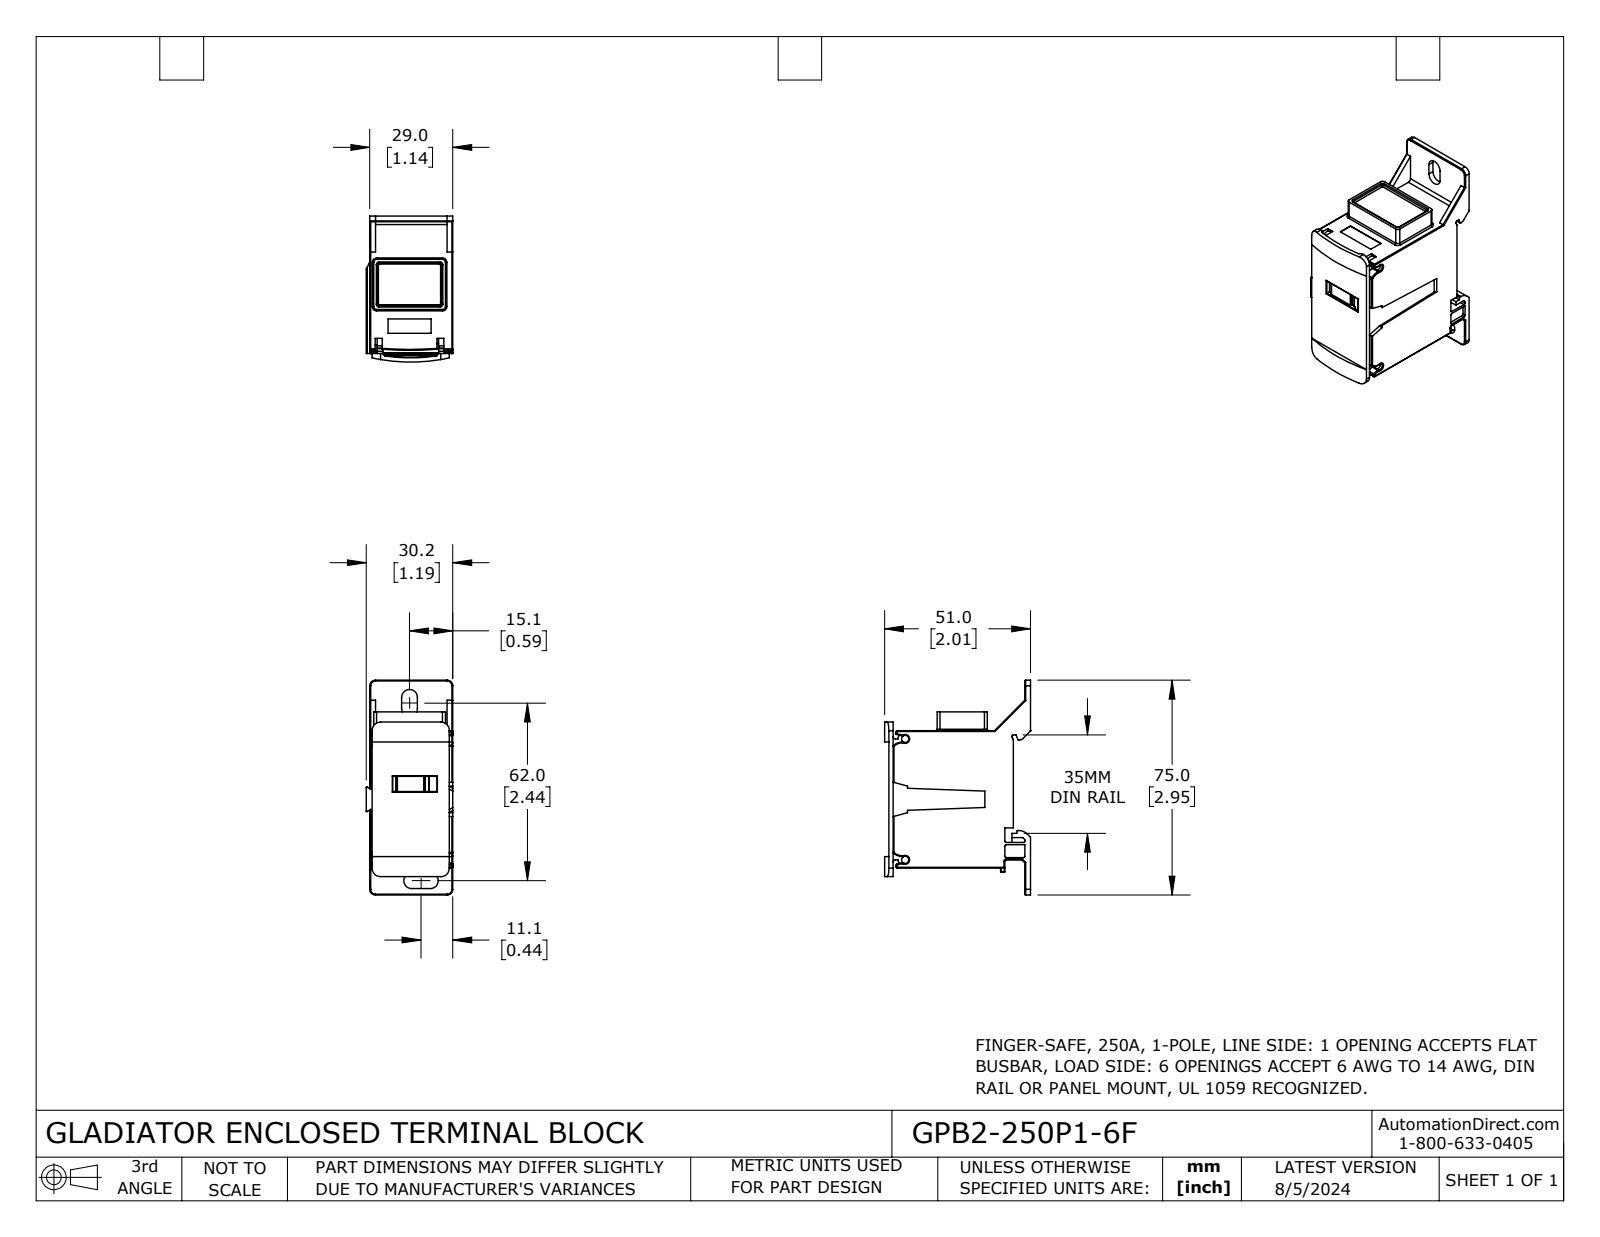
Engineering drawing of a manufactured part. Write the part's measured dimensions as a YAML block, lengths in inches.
part_name: "GPB2-250P1-6F"
step_written_by: "SolidWorks 2023 (CONFIG_CONTROL_DESIGN)"
units: inches
bodies: {solids: 1, faces: 464, planar: 181, cylindrical: 203, other: 80}
overall_size: [2.953, 2.008, 1.189]
volume: 3.936
surface_area: 23.63
round_holes:
  - {diameter: 0.098, count: 2}
  - {diameter: 0.394, count: 2}
partial_cylinders:
  - {radius: 0.008, count: 35}
  - {radius: 0.02, count: 30}
  - {radius: 0.012, count: 27}
  - {radius: 0.039, count: 5}
  - {radius: 0.079, count: 5}
  - {radius: 0.197, count: 5}
  - {radius: 0.108, count: 4}
  - {radius: 0.118, count: 4}
face_to_face_distances: [1.142, 1.949, 0.079, 0.236, 1.713, 1.89, 0.039, 0.157, 1.87, 1.85]
hole_center_spacings: [0.63, 1.661]
